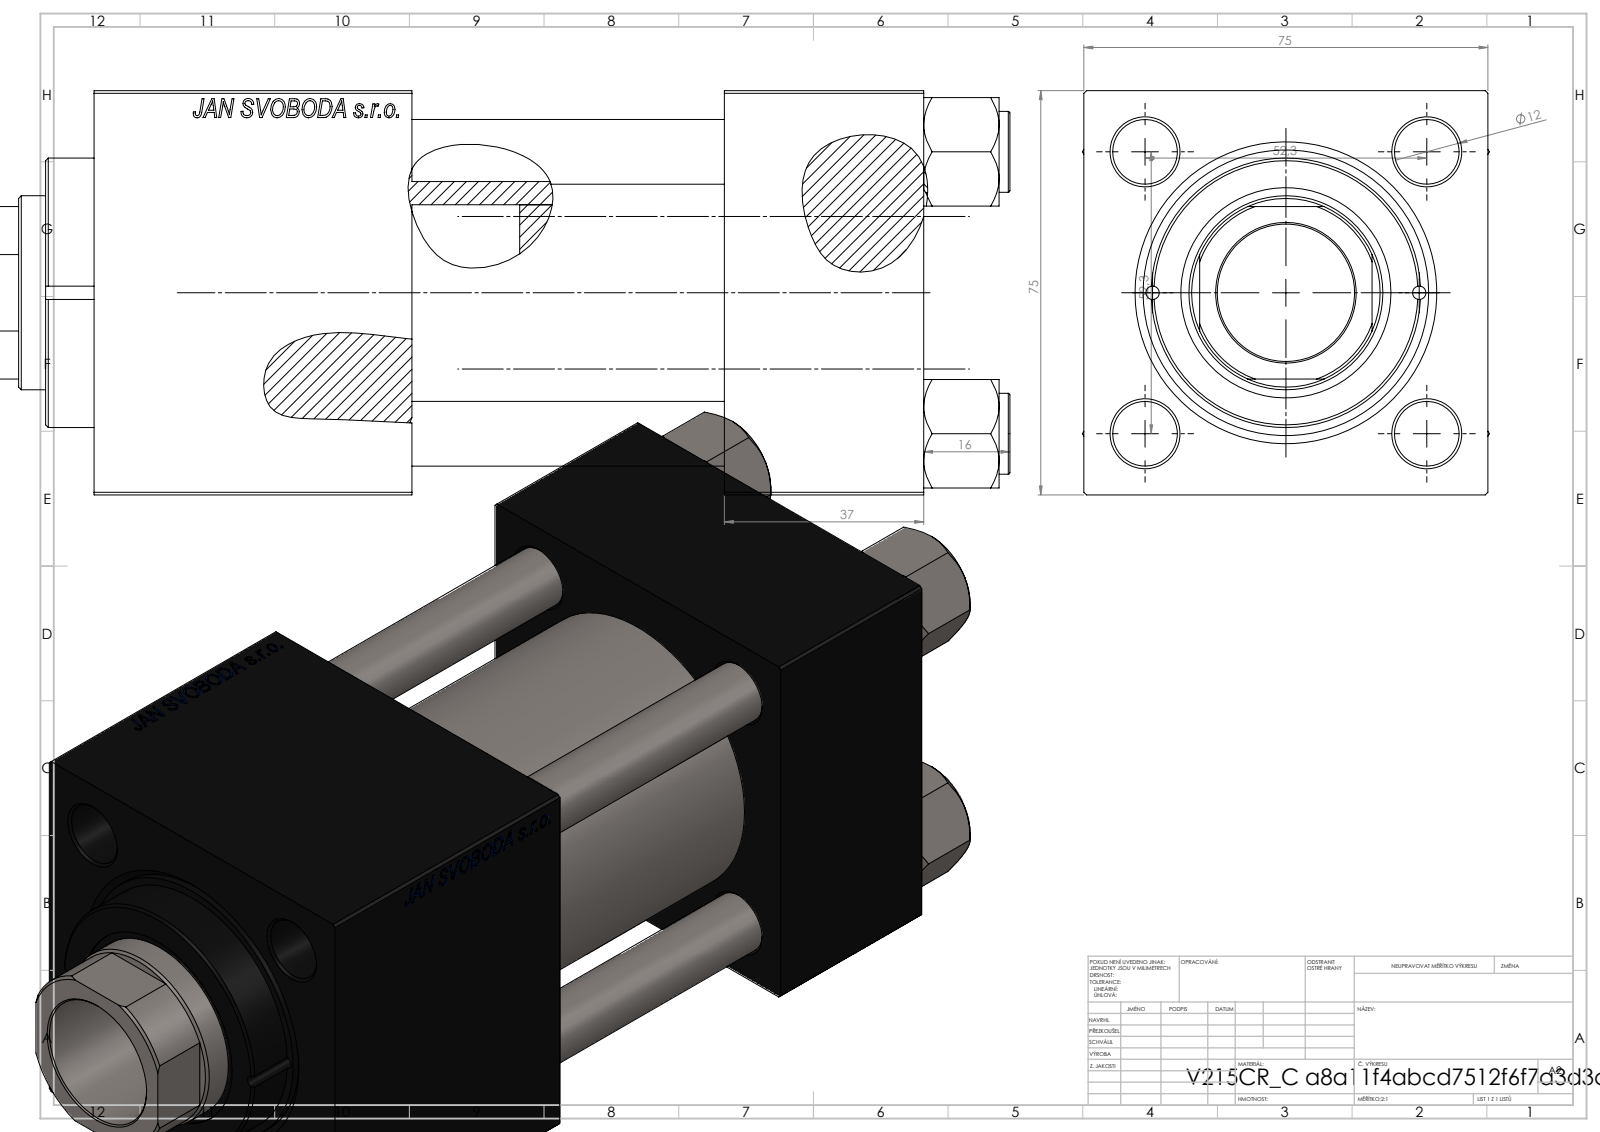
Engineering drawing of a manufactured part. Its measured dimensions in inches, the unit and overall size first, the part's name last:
Units: inches
Overall size (bounding box): 7.677 × 2.974 × 2.953
Round holes (diameter × count): ⌀0.472 ×4, ⌀0.098 ×2, ⌀0.276 ×2, ⌀0.825 ×2, ⌀1.181 ×2, ⌀1.004 ×1, ⌀1.417 ×1, ⌀1.535 ×1, ⌀1.614 ×1, ⌀2.087 ×1
Round bosses / shafts (diameter × count): ⌀0.591 ×4, ⌀2.205 ×1, ⌀1.969 ×1
Partial cylindrical surfaces — rounded edges, fillets, slot ends (radius × count): R0.689 ×1
Main face-to-face distances: 2.953, 1.457, 3.74, 2.283, 6.063, 4.606, 2.323, 4.933, 3.476, 1.193
Hole centre spacings: 1.031, 1.456, 2.059, 2.253, 0.974, 2.912, 1.949, 3.681
Volume: 41.86 in³ · Surface area: 241.2 in²
Bodies: 11 solids, 1154 faces (528 planar, 90 cylindrical, 536 other)
Part name (STEP PRODUCT): V215CR_VCP_C; V215CR_C_TYCINKA; NUT_M5_C; V215CR_C_Body (+1 more)
STEP written by: SolidWorks 2019 (CONFIG_CONTROL_DESIGN)
